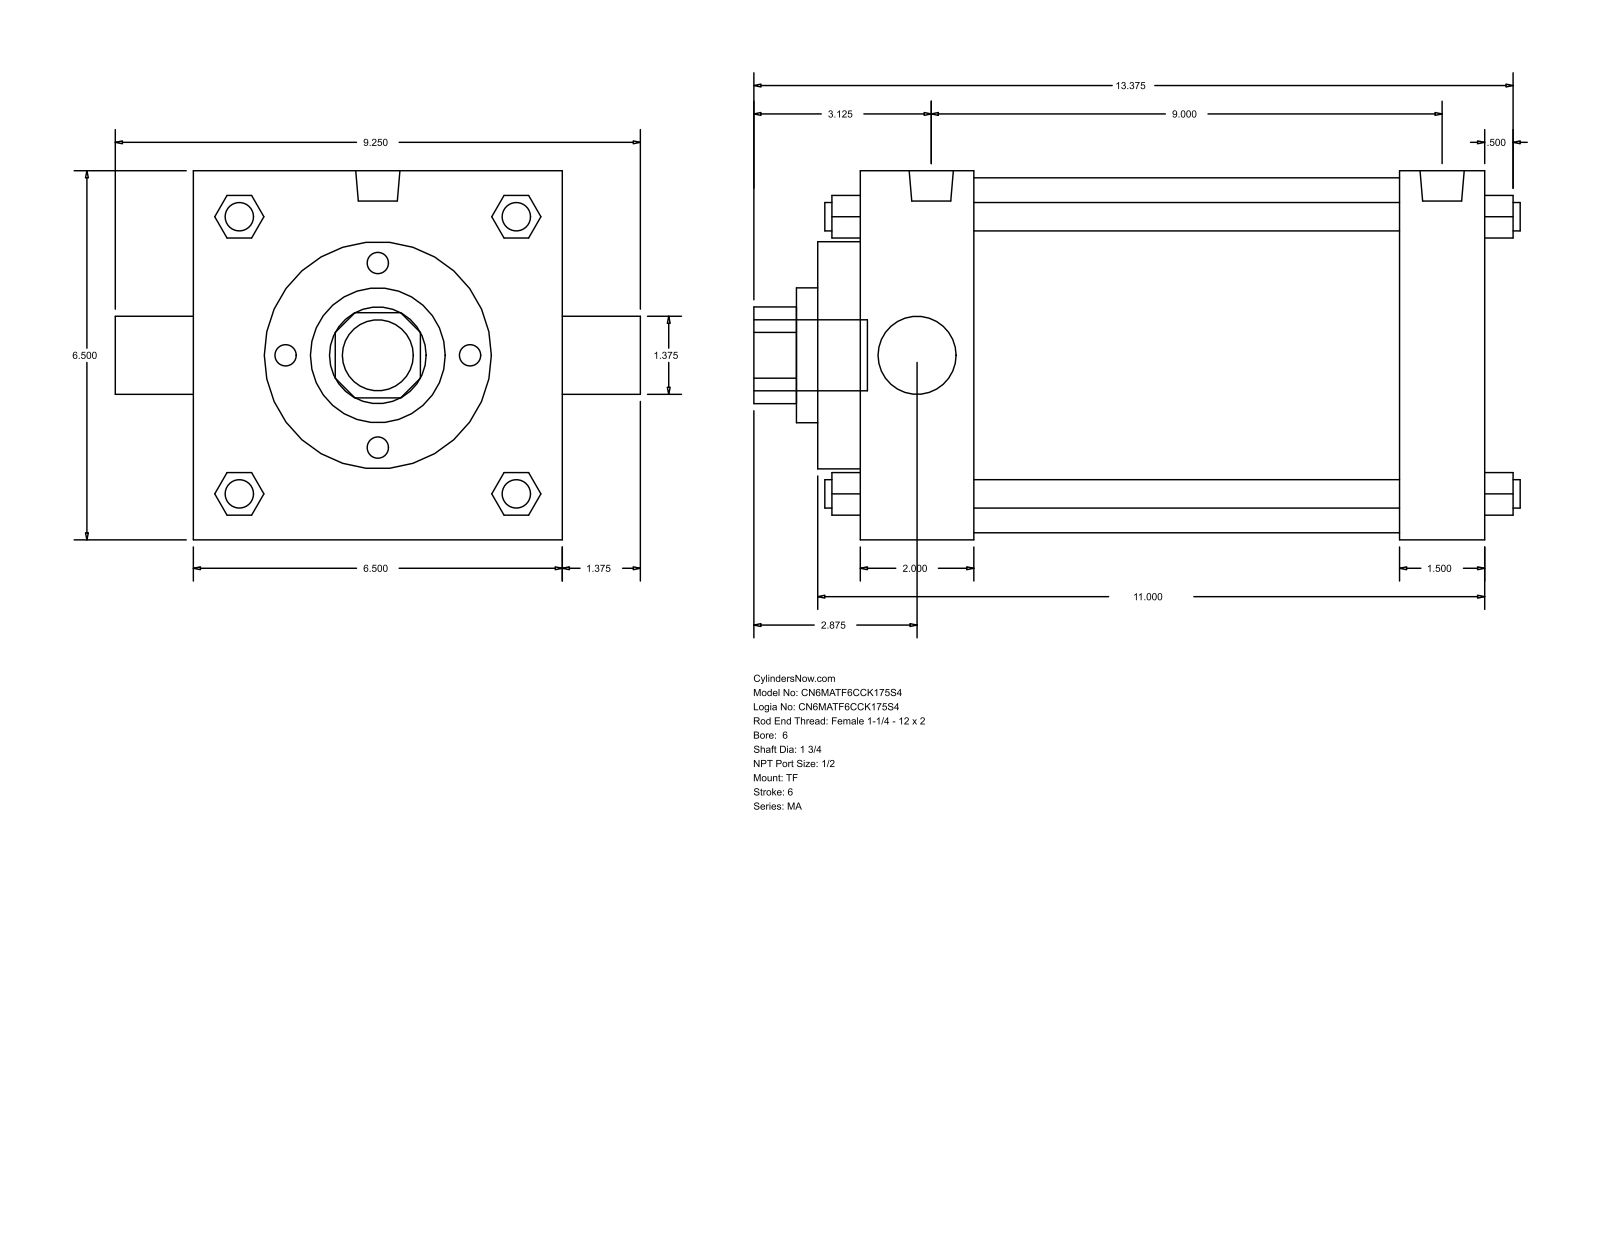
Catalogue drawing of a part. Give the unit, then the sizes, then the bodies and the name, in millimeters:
Units: millimetres
Overall size (bounding box): 342.9 × 234.95 × 165.1
Round holes (diameter × count): ⌀34.92 ×1, ⌀44.45 ×1, ⌀60.33 ×1, ⌀101.6 ×1, ⌀158.75 ×1
Round bosses / shafts (diameter × count): ⌀12.7 ×4, ⌀17.46 ×3, ⌀19.77 ×2, ⌀31.75 ×1
Partial cylindrical surfaces — rounded edges, fillets, slot ends (radius × count): R21.63 ×1
Main face-to-face distances: 165.1, 279.4, 19.05, 50.8, 241.31, 228.6, 190.51, 38.09, 69.85, 260.36
Bodies: 0 solids, 122 faces (93 planar, 29 cylindrical, 0 other)
Part name (STEP PRODUCT): MA_TF__0600_1.75
STEP written by: GSSL Pune (CONFIG_CONTROL_DESIGN)
